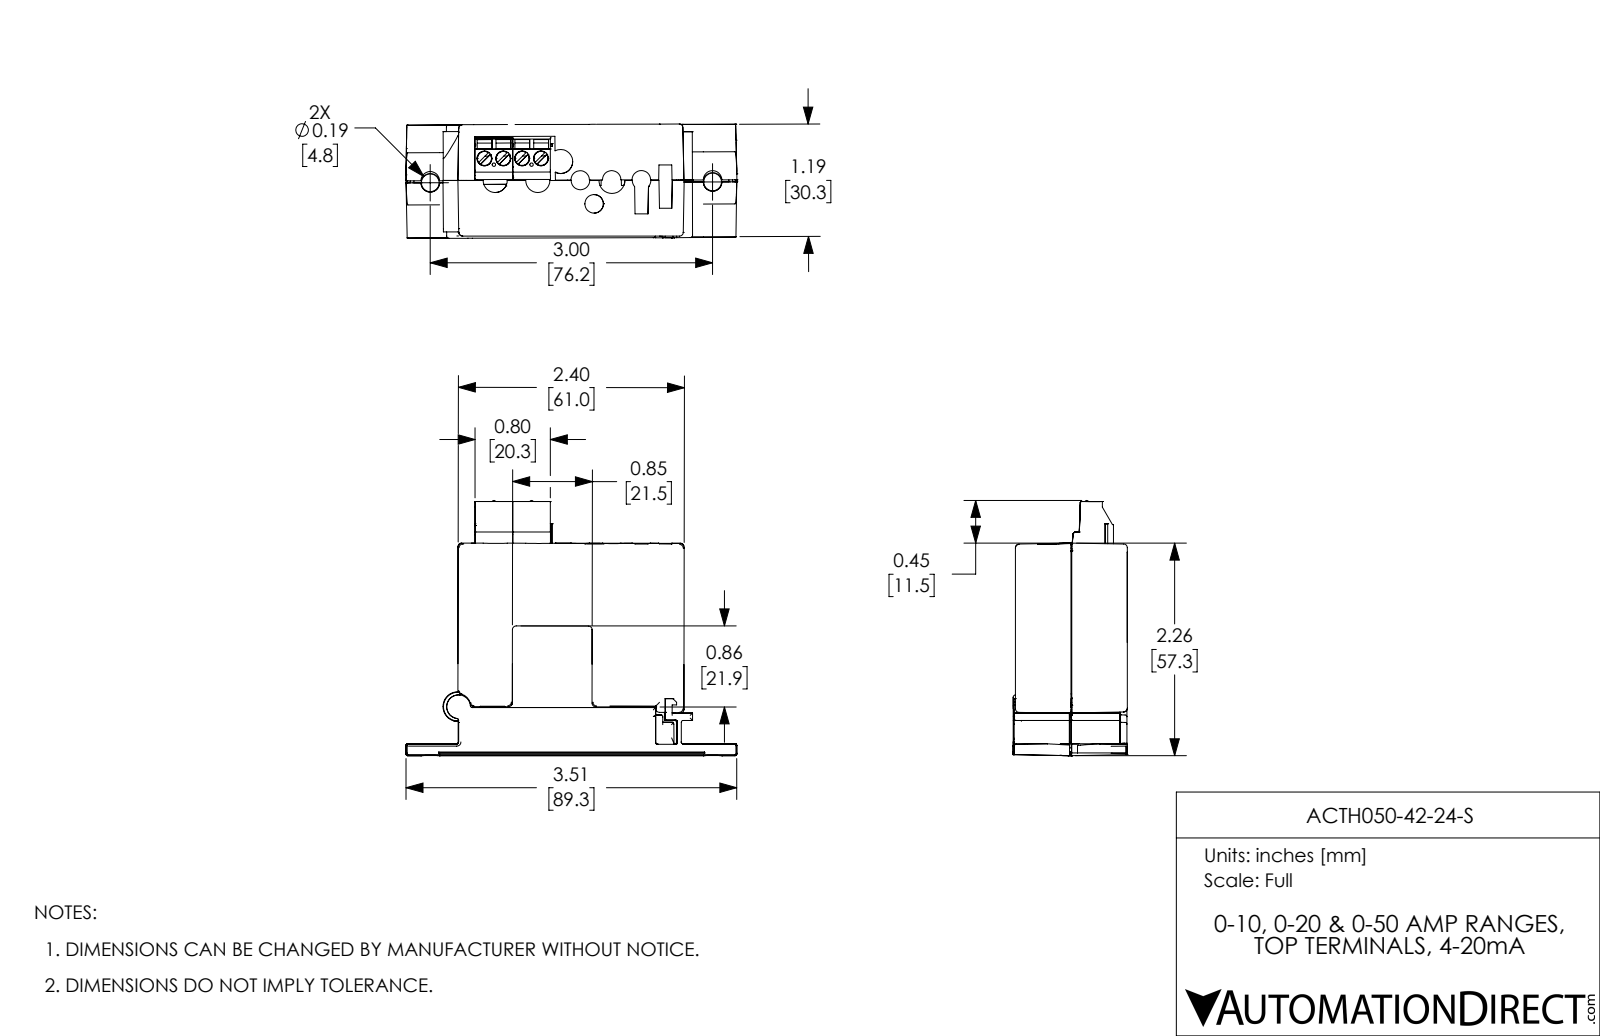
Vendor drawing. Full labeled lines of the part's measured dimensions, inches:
Part name (STEP PRODUCT): ACTH050-42-24-S
STEP written by: SolidWorks 2017 (AUTOMOTIVE_DESIGN)
Units: inches
Bodies: 6 solids, 1248 faces (801 planar, 266 cylindrical, 181 other)
Overall size (bounding box): 3.516 × 2.71 × 1.207
Volume: 5.949 in³ · Surface area: 83.12 in²
Round holes (diameter × count): ⌀0.157 ×4, ⌀0.197 ×3, ⌀0.055 ×2, ⌀0.018 ×1
Round bosses / shafts (diameter × count): ⌀0.15 ×4, ⌀0.051 ×4, ⌀0.306 ×1, ⌀0.018 ×1
Partial cylindrical surfaces — rounded edges, fillets, slot ends (radius × count): R0.02 ×52, R0.039 ×39, R0.006 ×22, R0.008 ×12, R0.025 ×11, R0.098 ×7, R0.004 ×4, R0.019 ×4
Main face-to-face distances: 0.079, 0.078, 0.858, 1.823, 1.425, 0.075, 2.275, 0.386, 0.591, 1.746
Hole centre spacings: 0.2, 0.392, 0.4, 0.065, 0.065, 0.196, 0.197, 0.2
